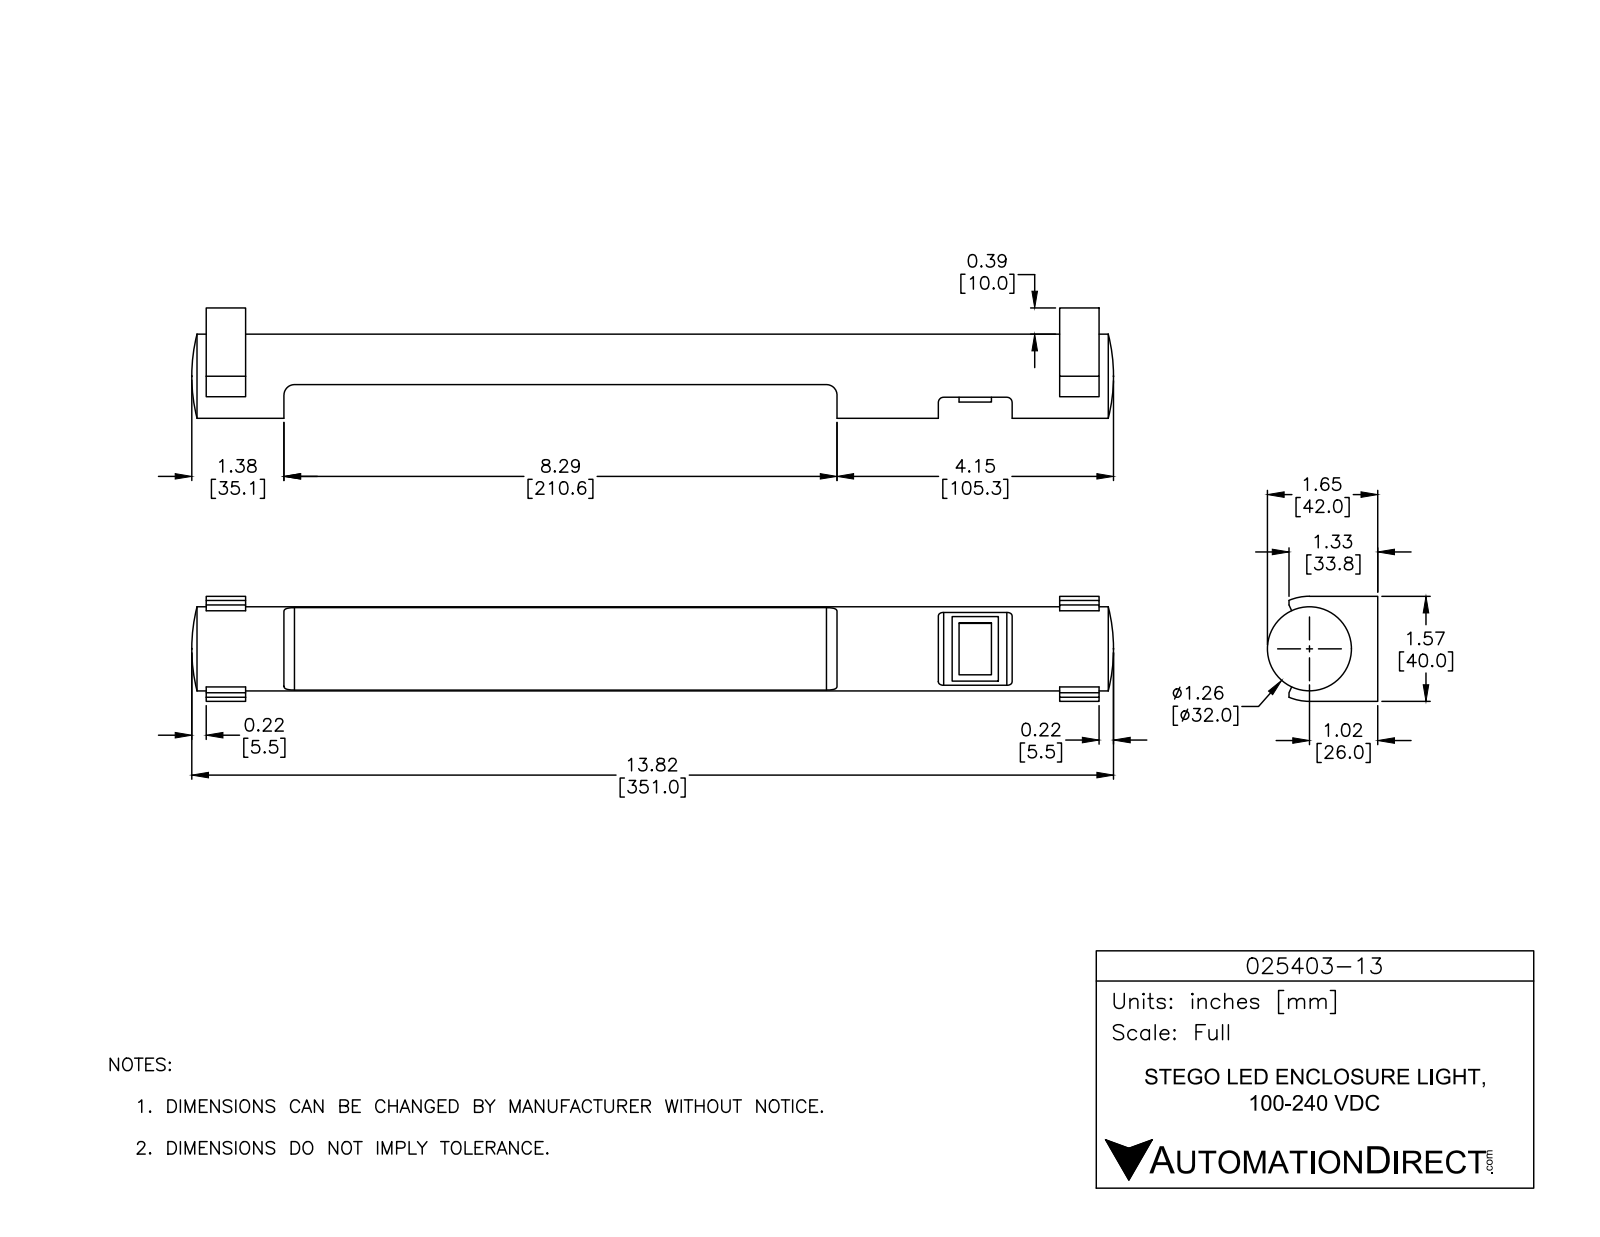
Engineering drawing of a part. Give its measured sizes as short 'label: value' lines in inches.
name: PRODUCT_NAME_1
written by: ACIS (CONFIG_CONTROL_DESIGN)
unit: in
bodies: 1 solid, 83 faces (51 planar, 28 cylindrical, 4 other)
size: 13.819 × 1.654 × 1.575
volume: 14.03 in³; area: 63.88 in²
bosses: 1× ⌀1.26
rounds: 4× R0.122, 2× R0.079, 2× R0.148, 2× R0.157, 1× R0.787, 1× R1.935
face distances: 12.795, 0.591, 1.15, 1.575, 13.386, 12.205, 0.098, 0.492, 0.295, 1.28
